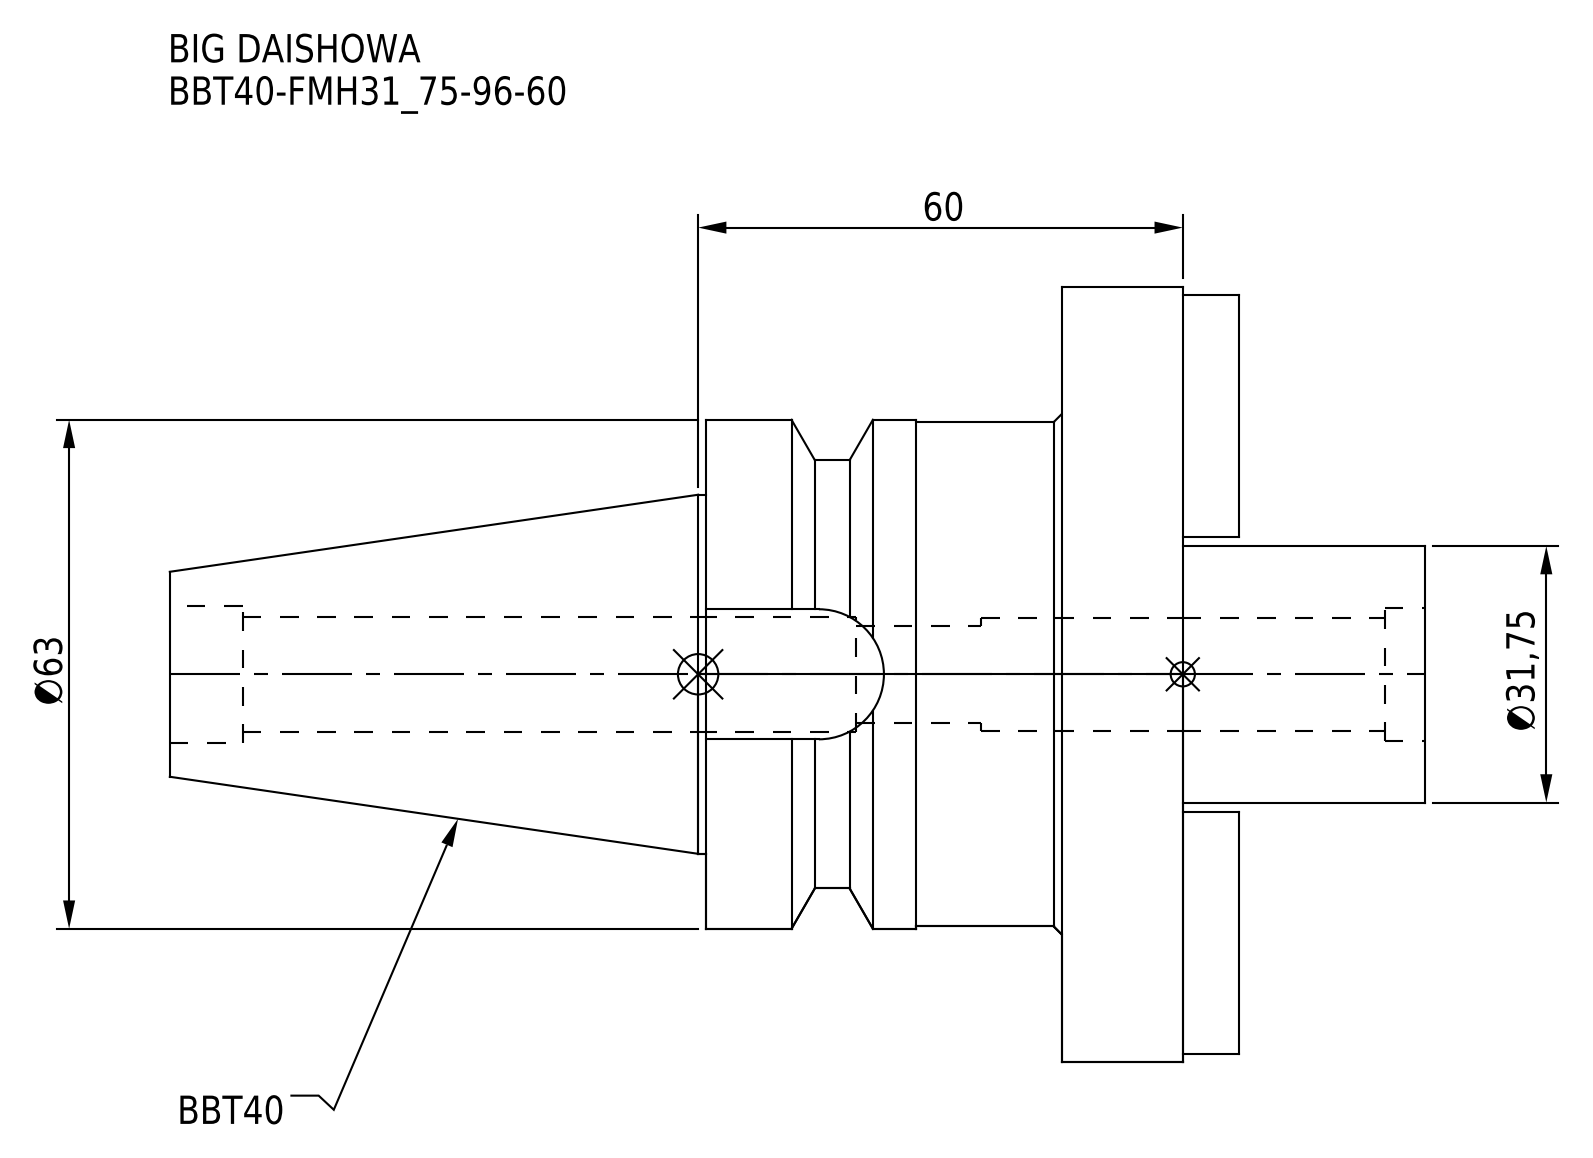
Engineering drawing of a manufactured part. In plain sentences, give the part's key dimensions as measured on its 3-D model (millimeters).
The part is named "BBT40-FMH31_75-96-60". Its 3-D file was written by "CREO PARAMETRIC BY PTC INC, 2016380 (AUTOMOTIVE_DESIGN)". It is 1 solid with 64 faces: 26 planar, 30 cylindrical and 8 other. Overall it measures 155.4 by 96 by 96 millimeters. Its volume is 303 798 cubic millimeters and its surface area 45 983 square millimeters. Round holes: 1 of diameter 12, 1 of diameter 14, 1 of diameter 14.2, 1 of diameter 16.5, 1 of diameter 17. Round bosses or shafts: 1 of diameter 96, 1 of diameter 63, 1 of diameter 62.4, 1 of diameter 53, 1 of diameter 44.45, 1 of diameter 31.75. Partial cylindrical surfaces (rounded edges, fillets, slot ends): 1 of radius 8.05. The main face-to-face distances are 15, 59, 44, 45, 7, 22, 66, 30, 16.15, 28.85.
